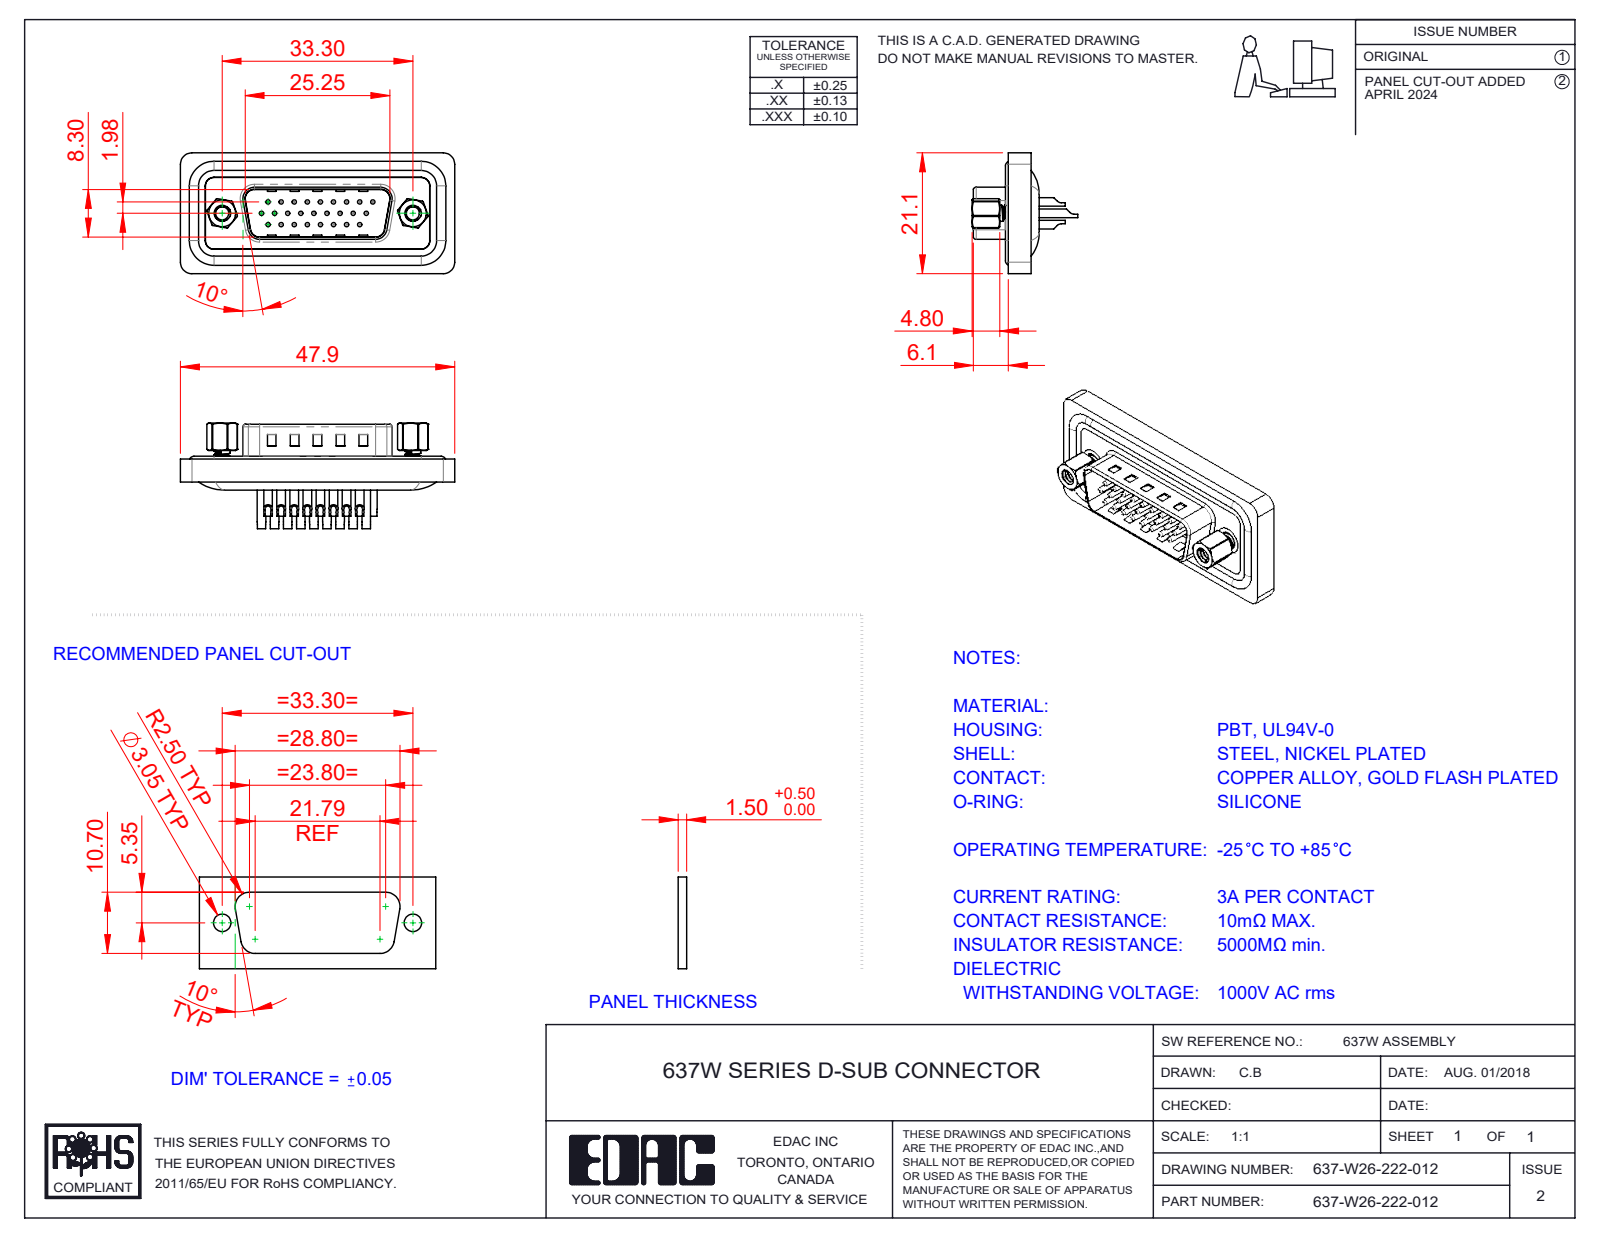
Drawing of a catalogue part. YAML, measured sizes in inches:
part_name: "637-W26-222-012; 637W 4-40 Hex Standoff; 637W 4-40 Threaded Rivet; 637W Waterproof Housing_26 Contacts (+5 more)"
step_written_by: "SolidWorks 2016 (CONFIG_CONTROL_DESIGN)"
units: inches
bodies: {solids: 34, faces: 1496, planar: 407, cylindrical: 680, other: 409}
overall_size: [1.885, 0.831, 0.719]
volume: 0.304
surface_area: 14.13
round_holes:
  - {diameter: 0.03, count: 26}
  - {diameter: 0.039, count: 26}
  - {diameter: 0.059, count: 26}
  - {diameter: 0.063, count: 26}
  - {diameter: 0.079, count: 26}
  - {diameter: 0.089, count: 2}
  - {diameter: 0.09, count: 2}
  - {diameter: 0.157, count: 2}
  - {diameter: 0.189, count: 2}
  - {diameter: 0.197, count: 2}
round_bosses_or_shafts:
  - {diameter: 0.059, count: 26}
  - {diameter: 0.063, count: 4}
  - {diameter: 0.193, count: 2}
  - {diameter: 0.11, count: 2}
  - {diameter: 0.197, count: 1}
partial_cylinders:
  - {radius: 0.079, count: 16}
  - {radius: 0.059, count: 14}
  - {radius: 0.02, count: 8}
  - {radius: 0.106, count: 6}
  - {radius: 0.035, count: 4}
  - {radius: 0.063, count: 4}
  - {radius: 0.169, count: 4}
  - {radius: 0.039, count: 3}
face_to_face_distances: [0.016, 0.063, 0.043, 0.114, 0.098, 0.02, 0.222, 0.608, 0.03, 0.157]
hole_center_spacings: [0.156, 0.09, 0.18, 0.238, 0.09, 0.324, 0.27, 0.238]
